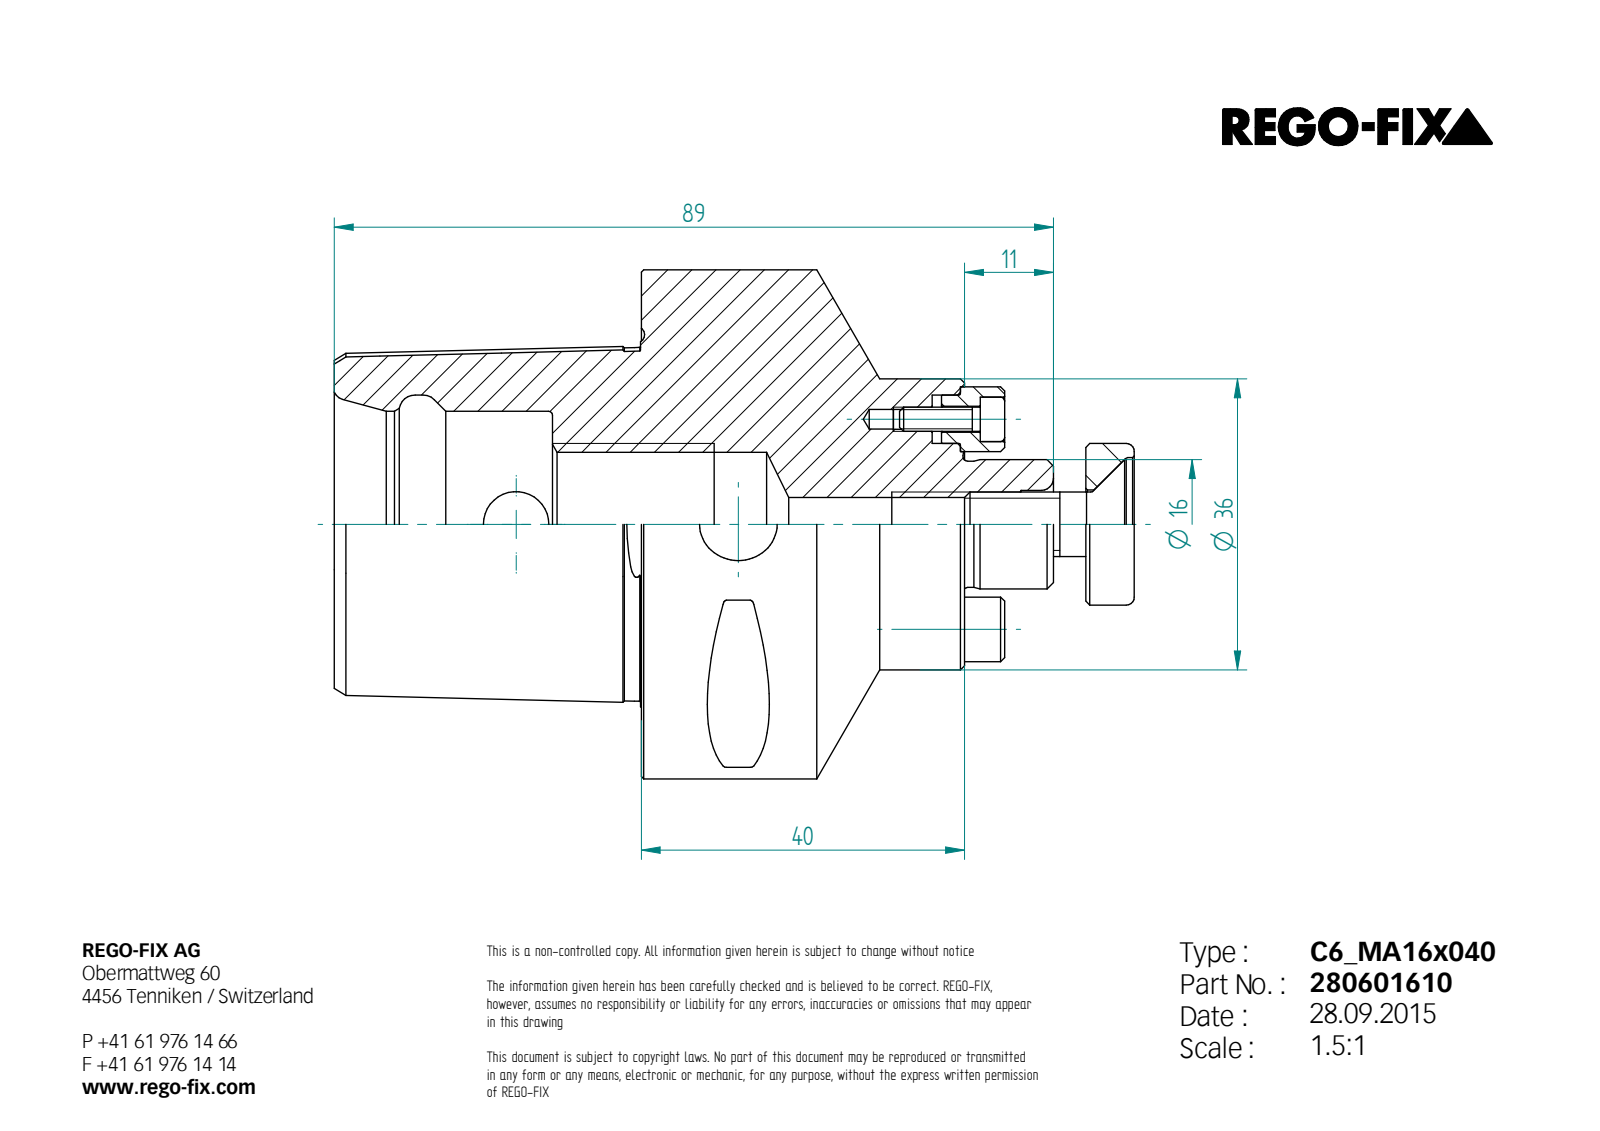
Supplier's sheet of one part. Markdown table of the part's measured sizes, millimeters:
| quantity | value |
| --- | --- |
| part name | 0003464; 0003381; 0007093; 0004885 (+1 more) |
| STEP written by | Unknown (AUTOMOTIVE_DESIGN) |
| units | millimeters |
| bodies | 7 solids, 235 faces (51 planar, 65 cylindrical, 119 other) |
| overall size | 99 × 63 × 63 |
| volume | 124 630 mm³ |
| surface area | 25 829 mm² |
| round holes (diameter × count) | 2.44 × 2, 2.46 × 2, 3.2 × 2, 6 × 2, 8 × 2, 4 × 1, 6.65 × 1, 8.1 × 1, 8.4 × 1, 8.5 × 1, 16.5 × 1, 17.84 × 1 |
| round bosses / shafts (diameter × count) | 5.5 × 2, 3 × 2, 63 × 1, 36 × 1, 20 × 1, 16 × 1, 15.6 × 1, 8 × 1 |
| partial cylindrical surfaces (radius × count) | 0.5 × 8, 5 × 1 |
| main face-to-face distances | 40, 38, 78, 11, 51, 24.89, 27, 15, 93, 66 |
| hole center spacings | 13, 26, 27.5 |
